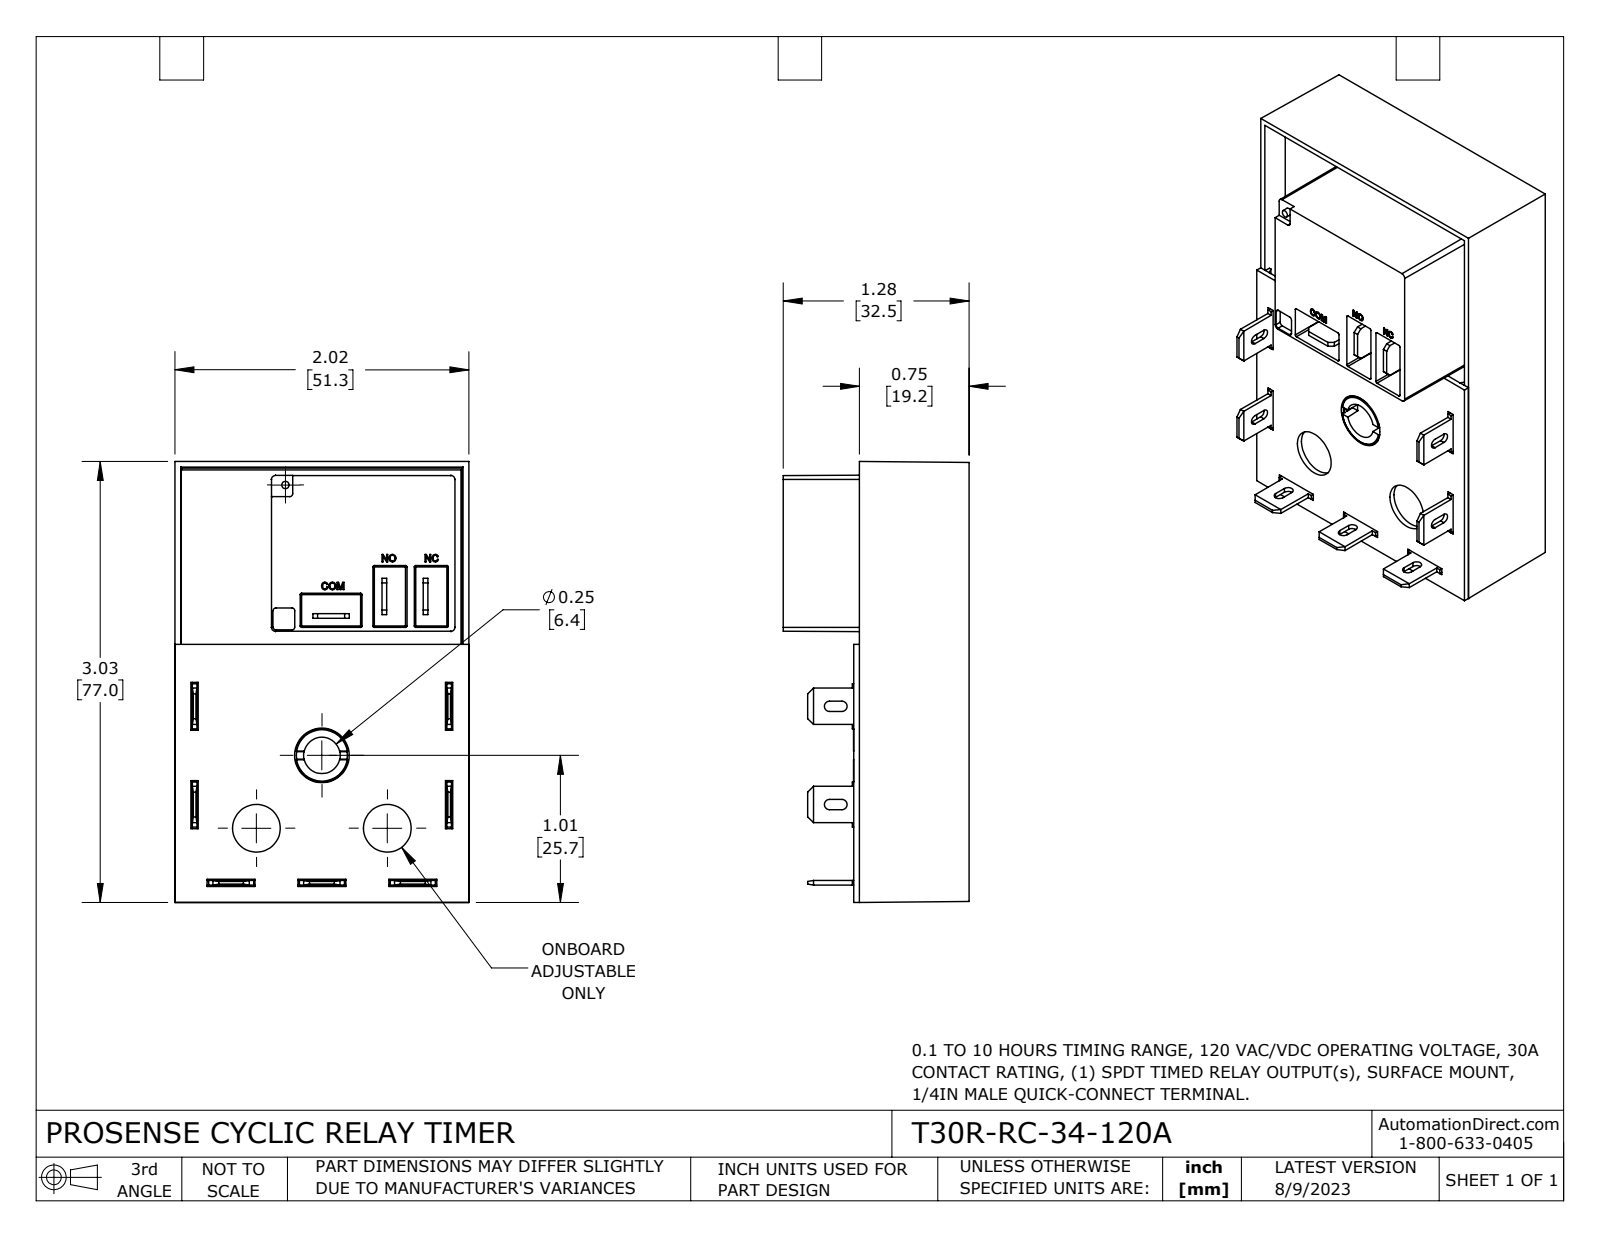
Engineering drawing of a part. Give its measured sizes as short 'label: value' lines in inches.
name: T30R-RC-34-120A
written by: SolidWorks 2021 (CONFIG_CONTROL_DESIGN)
unit: in
bodies: 11 solids, 622 faces (493 planar, 69 cylindrical, 60 other)
size: 3.03 × 2.02 × 1.278
volume: 4.946 in³; area: 66.59 in²
holes: 2× ⌀0.328, 1× ⌀0.35, 1× ⌀0.375
bosses: 1× ⌀0.365, 1× ⌀0.05
rounds: 21× R0.01, 15× R0.02, 10× R0.035
face distances: 0.059, 0.557, 0.498, 0.04, 0.754, 0.695, 0.197, 0.039, 0.734, 0.793
hole spacings: 0.673, 0.9
